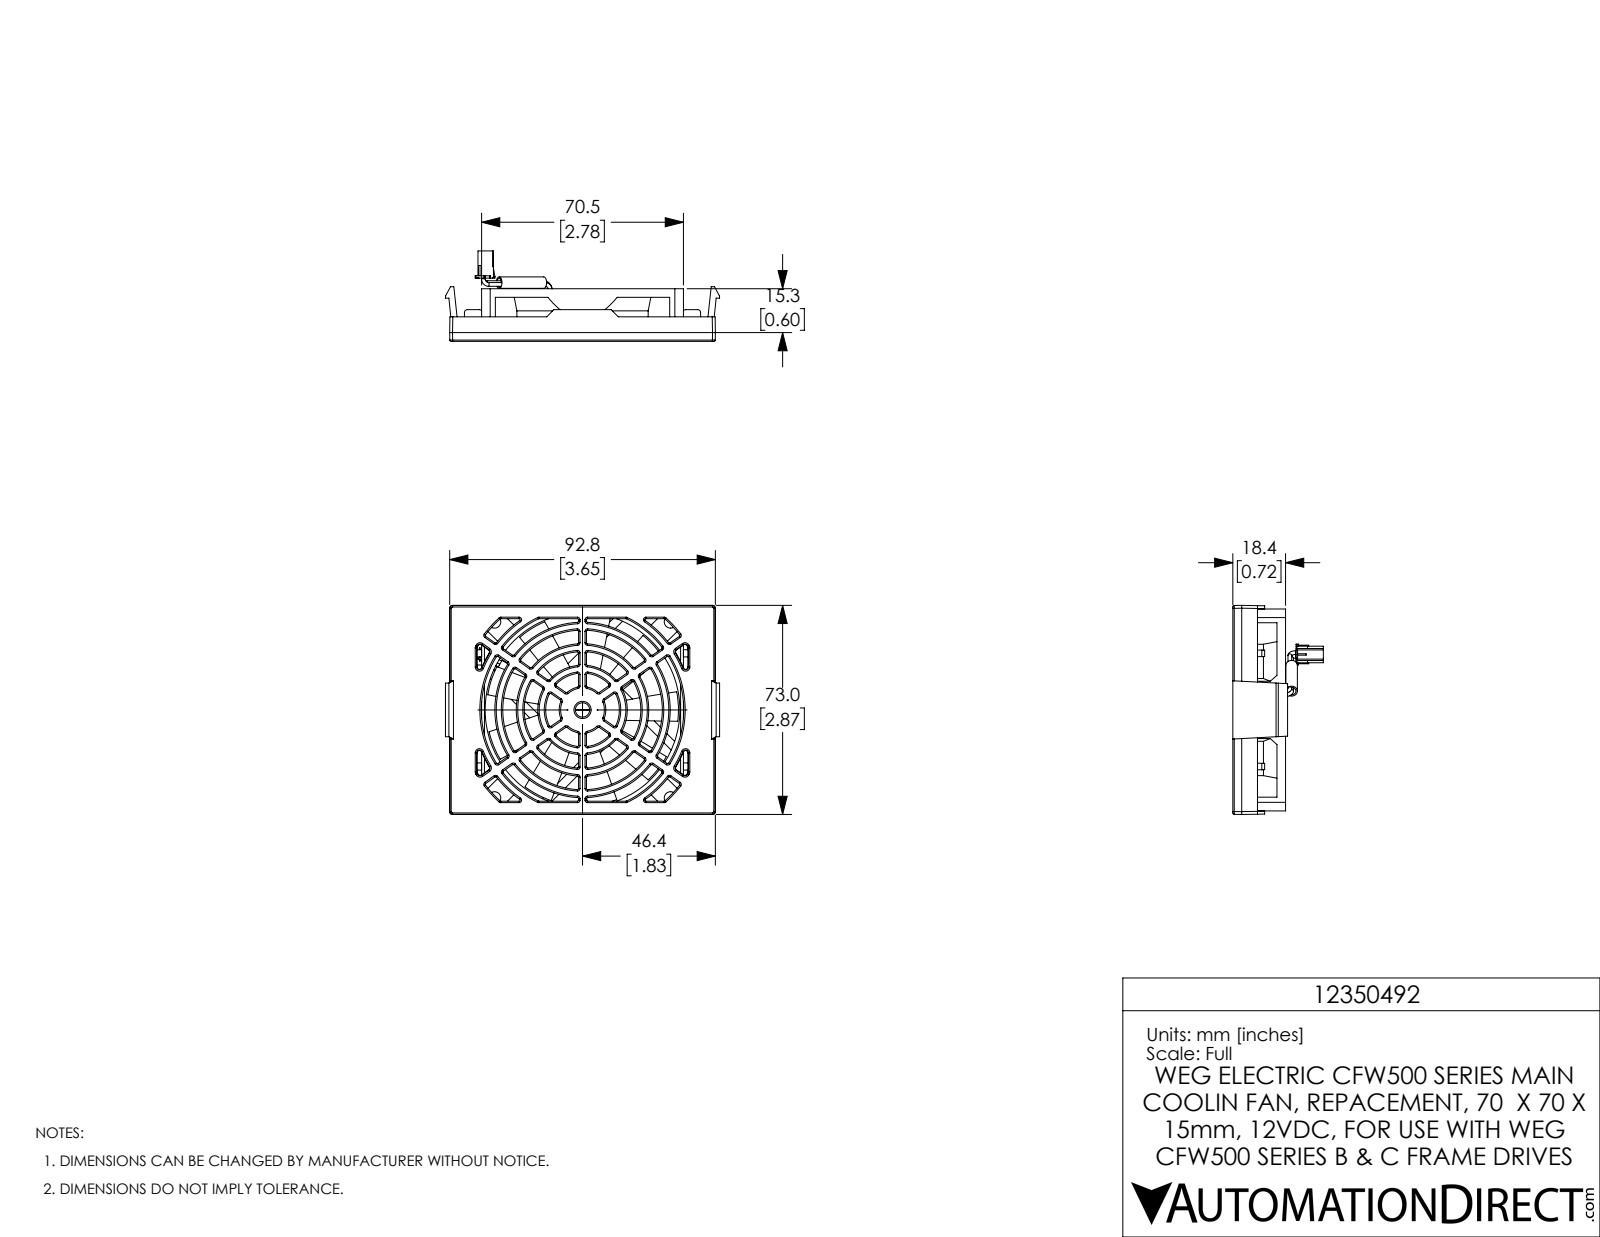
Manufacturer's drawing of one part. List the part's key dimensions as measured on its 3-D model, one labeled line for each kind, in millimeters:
Part name (STEP PRODUCT): 12350492
STEP written by: SolidWorks 2017 (AUTOMOTIVE_DESIGN)
Units: millimetres
Bodies: 6 solids, 1752 faces (656 planar, 311 cylindrical, 785 other)
Overall size (bounding box): 95.7 × 73 × 31.6
Volume: 41 000 mm³ · Surface area: 42 410 mm²
Round holes (diameter × count): ⌀4.4 ×4, ⌀3 ×1, ⌀68 ×1
Round bosses / shafts (diameter × count): ⌀1.3 ×4, ⌀30 ×1, ⌀5 ×1, ⌀4 ×1
Partial cylindrical surfaces — rounded edges, fillets, slot ends (radius × count): R0.5 ×50, R0.1 ×16, R0.3 ×16, R1 ×12, R0.3 ×4, R3 ×4, R33.5 ×1, R36 ×1
Main face-to-face distances: 3.1, 18.4, 3, 2, 15.3, 70.5, 1, 2.5, 10.3, 12.3
Hole centre spacings: 43.5, 61.5, 87
